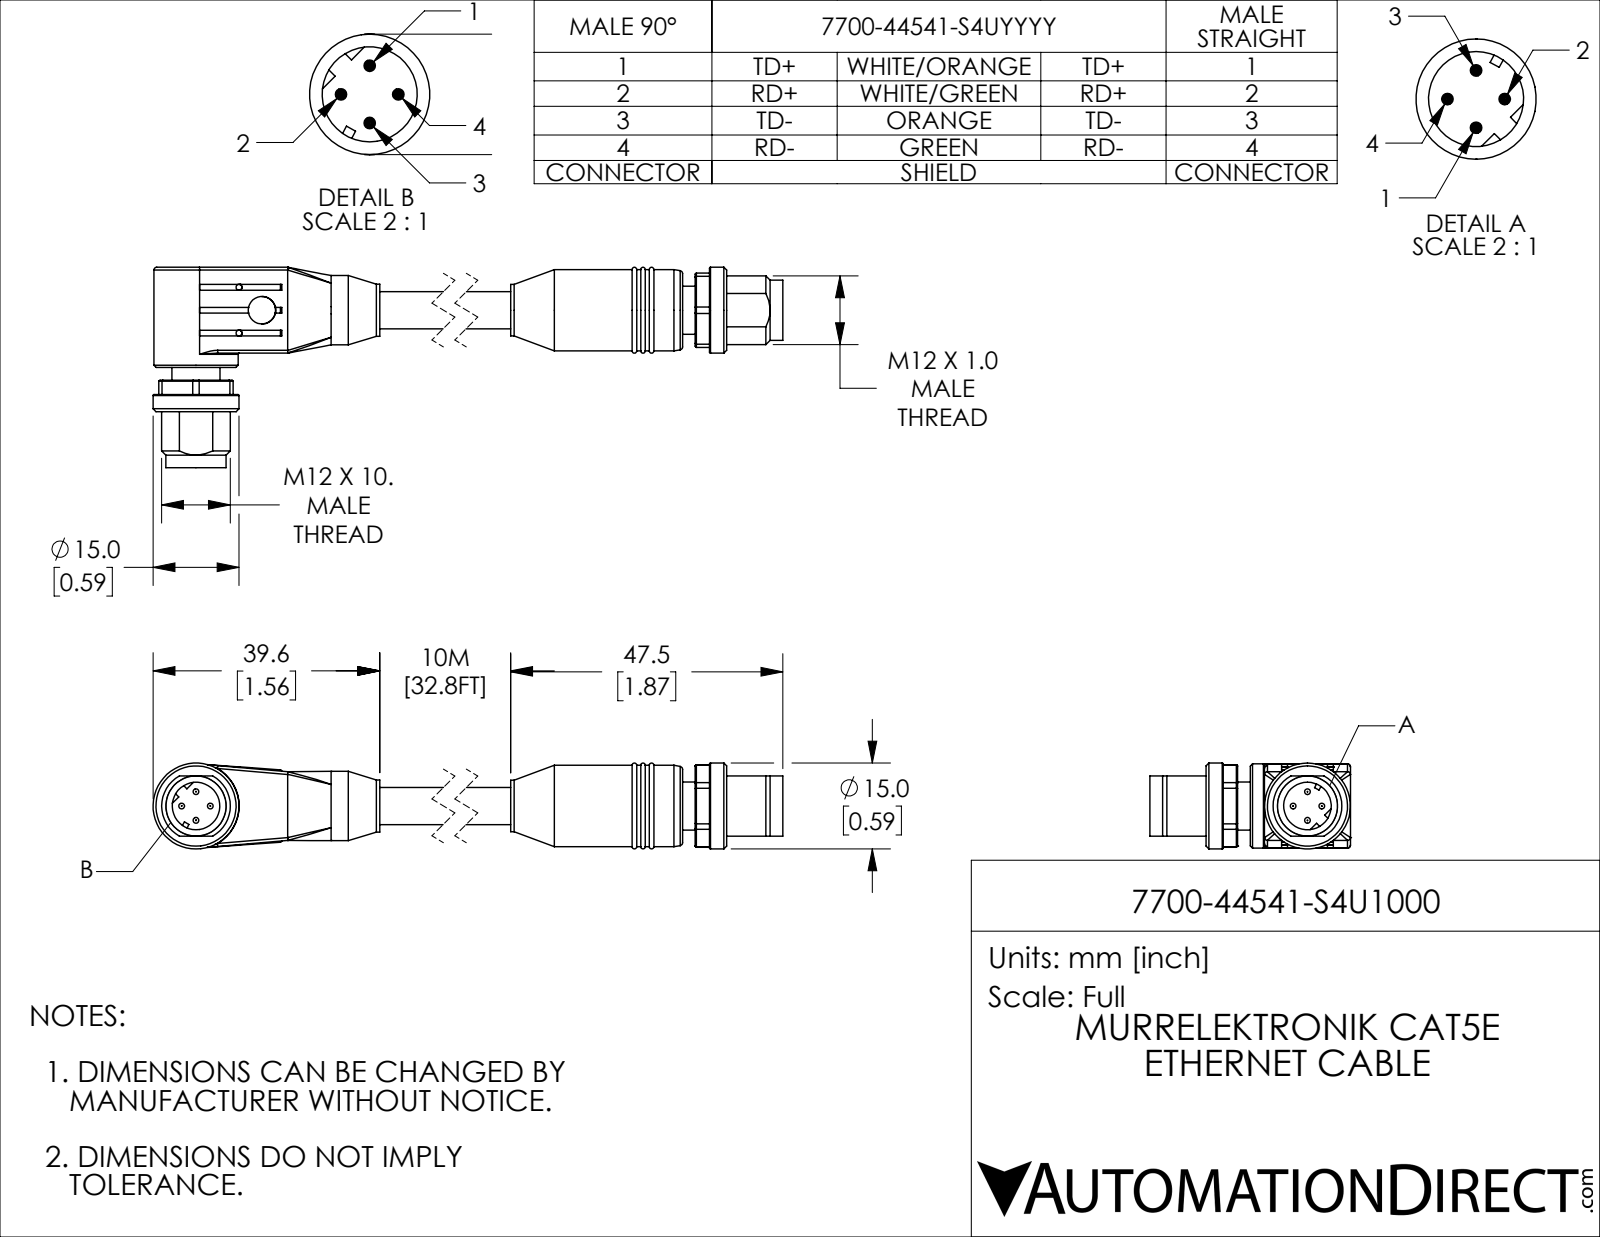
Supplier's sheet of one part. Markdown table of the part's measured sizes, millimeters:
| quantity | value |
| --- | --- |
| part name | 7700-44541-S4U1000; 7700-44541-S4U1000_1; 7700-44541-S4U1000_2 |
| STEP written by | SolidWorks 2021 (CONFIG_CONTROL_DESIGN) |
| units | millimeters |
| bodies | 2 solids, 284 faces (114 planar, 90 cylindrical, 80 other) |
| overall size | 133.5 × 35 × 15 |
| volume | 15 600 mm³ |
| surface area | 7 045 mm² |
| round holes (diameter × count) | 1 × 4, 8.3 × 2, 4.8 × 1 |
| round bosses / shafts (diameter × count) | 1 × 8, 15 × 2, 10.5 × 2, 8.4 × 2, 14.7 × 1, 14.2 × 1, 12.1 × 1, 9.1 × 1 |
| partial cylindrical surfaces (radius × count) | 0.5 × 4, 0.3 × 2, 6 × 2, 7.2 × 2 |
| main face-to-face distances | 17.5, 2.2, 2.5, 4.7, 15, 0.9, 6.4, 8.6, 5.5, 7.7 |
| hole center spacings | 8 |
